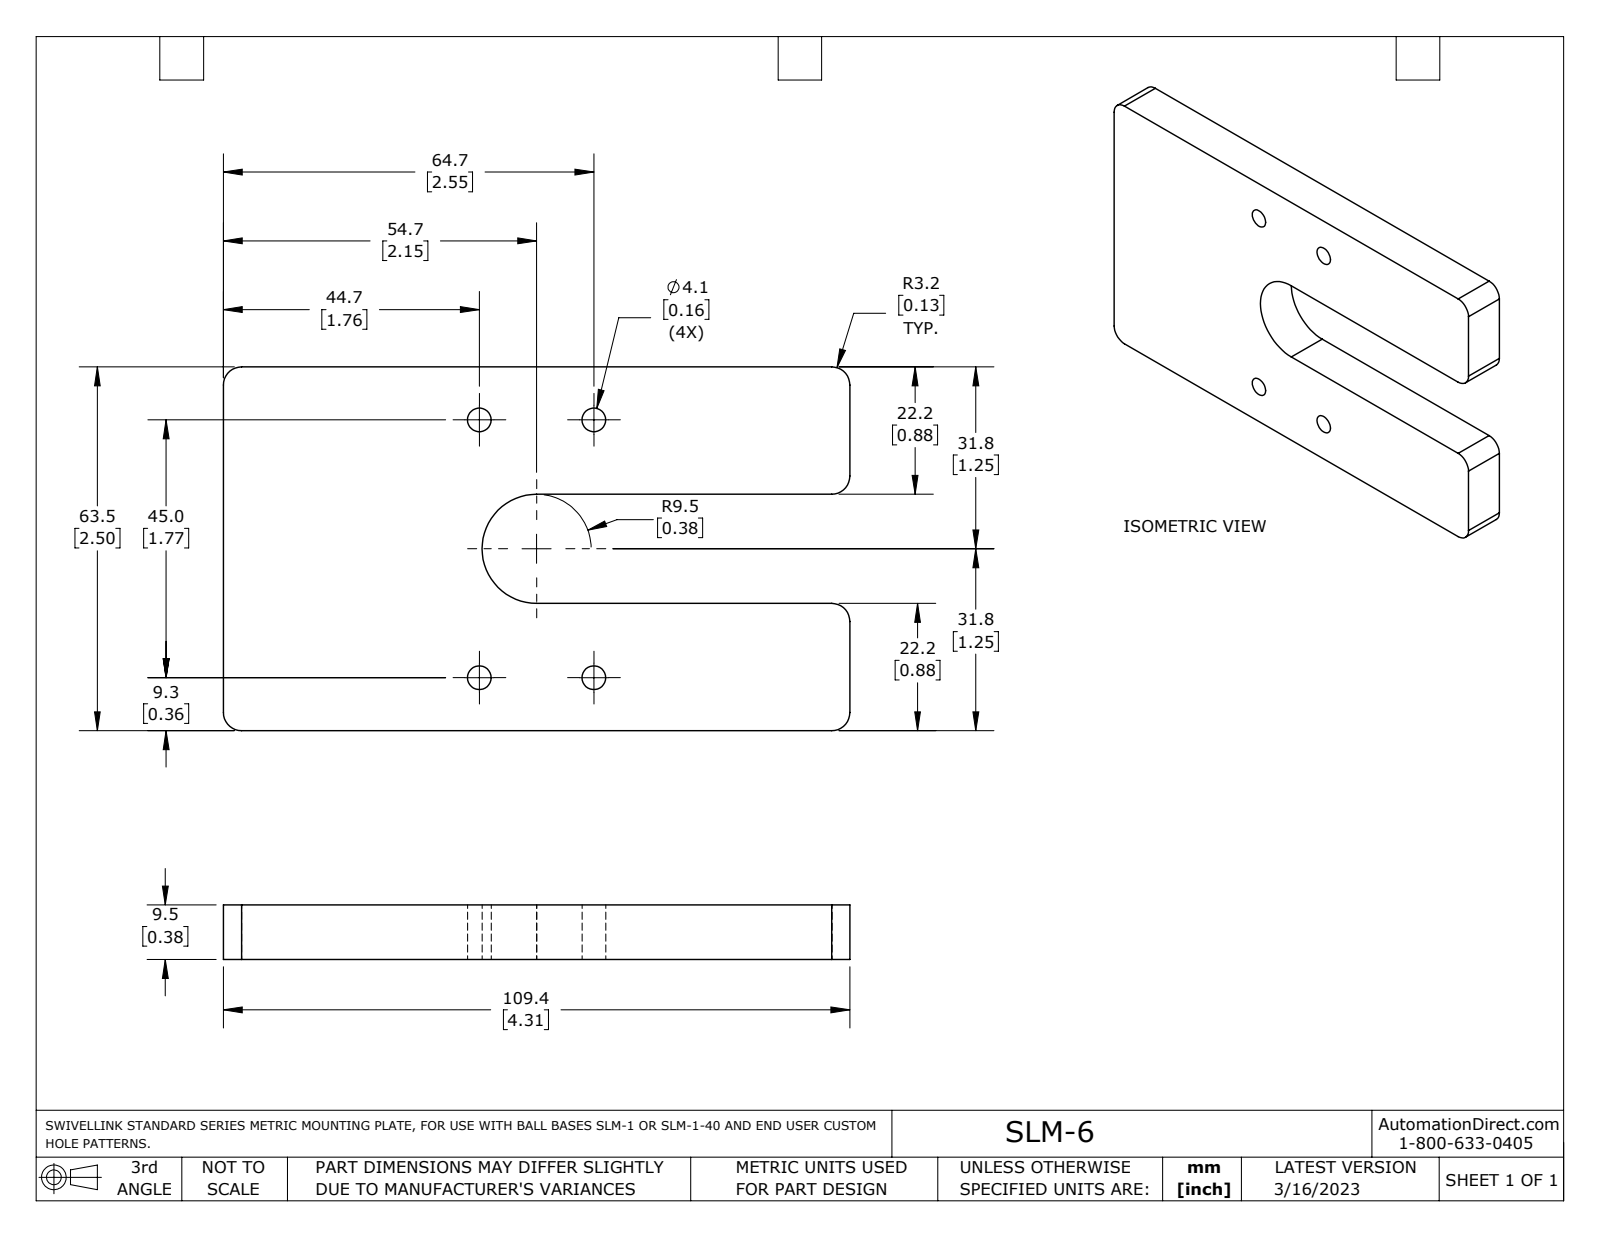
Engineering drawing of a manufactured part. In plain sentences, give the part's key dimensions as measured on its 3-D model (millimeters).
The part is named "SLM-6". Its 3-D file was written by "SolidWorks 2021 (AUTOMOTIVE_DESIGN)". It is 1 solid with 20 faces: 9 planar, 11 cylindrical and 0 other. Overall it measures 109.4 by 63.5 by 9.5 millimeters. Its volume is 54 260 cubic millimeters and its surface area 16 250 square millimeters. Round holes: 4 of diameter 4.1. Partial cylindrical surfaces (rounded edges, fillets, slot ends): 6 of radius 3.2, 1 of radius 9.5. The main face-to-face distances are 9.5, 22.2, 41.3, 63.5, 19.1, 109.4. The hole center spacings are 20, 45, 49.3.
